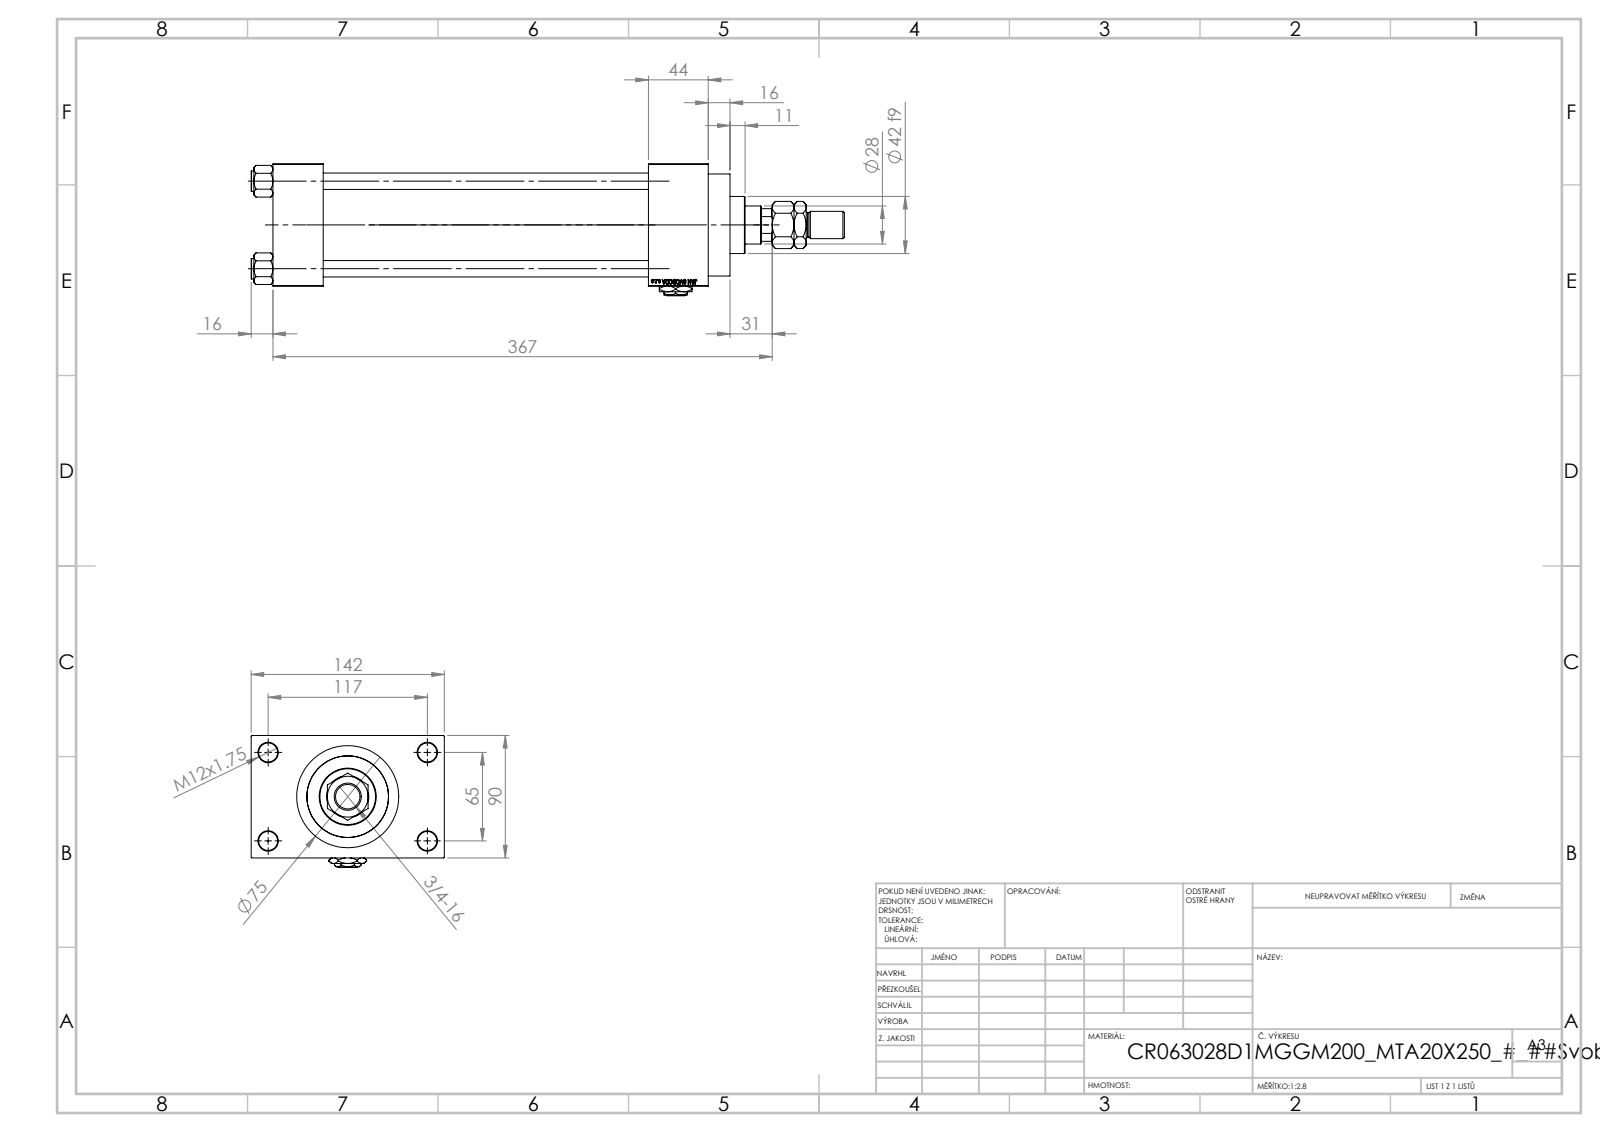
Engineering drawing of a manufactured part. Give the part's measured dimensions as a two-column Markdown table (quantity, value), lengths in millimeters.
| quantity | value |
| --- | --- |
| part name | Zatka_pro_OIL_PORT; V215CR_D_TYCINKA; V215_VC_A; NUT_M5_D (+3 more) |
| STEP written by | SolidWorks 2019 (CONFIG_CONTROL_DESIGN) |
| units | millimeters |
| bodies | 13 solids, 1201 faces (536 planar, 97 cylindrical, 568 other) |
| overall size | 436 × 142 × 97 |
| volume | 1 434 000 mm³ |
| surface area | 323 942 mm² |
| round holes (diameter × count) | 12 × 4, 14 × 4, 7 × 2, 20.96 × 2, 30 × 2, 18.5 × 1, 28 × 1, 31 × 1, 50 × 1, 60 × 1, 63 × 1 |
| round bosses / shafts (diameter × count) | 15 × 4, 75 × 1, 69 × 1, 42 × 1, 20 × 1, 18 × 1 |
| partial cylindrical surfaces (radius × count) | 13.5 × 1 |
| main face-to-face distances | 90, 239, 37, 276, 283, 320, 44, 116, 26, 142 |
| hole center spacings | 26.35, 45.47, 64.3, 66.92, 69.81, 90.65, 111.34, 65 |
